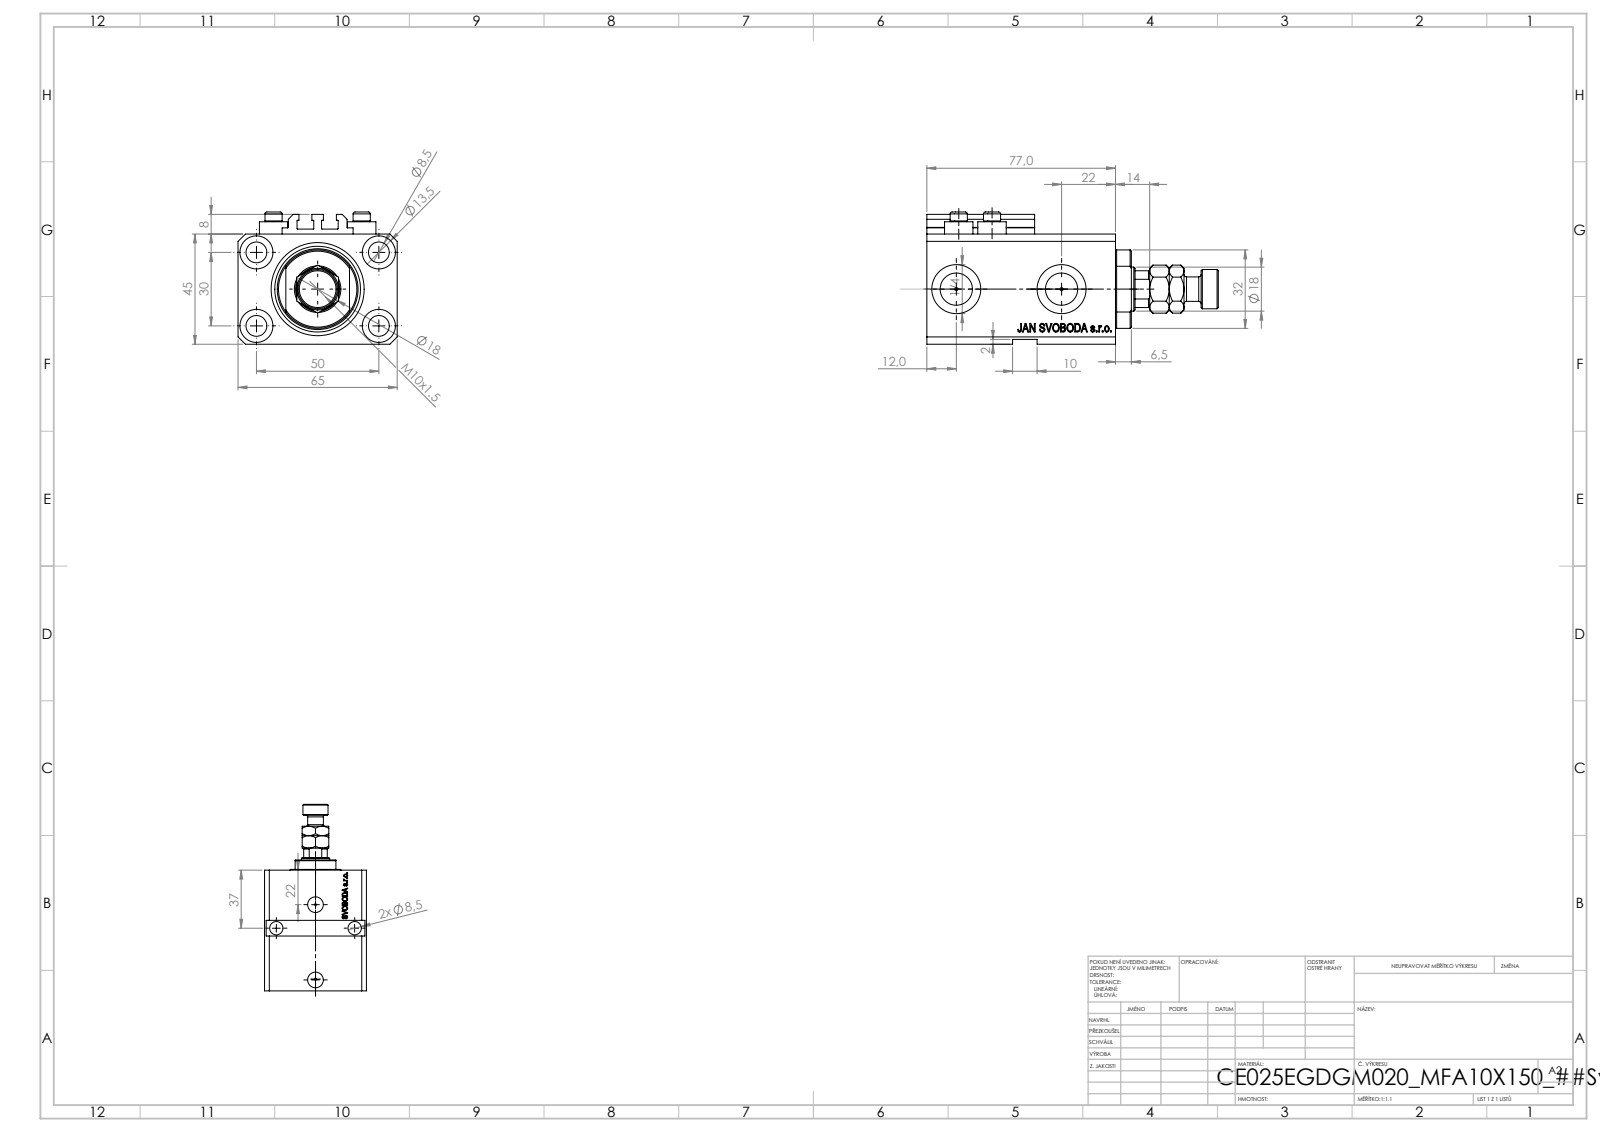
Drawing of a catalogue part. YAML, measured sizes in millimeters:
part_name: "V250CE_E_Body; ALLEN BOLT V250CE; V250CE_VC_E; V250CE_C_VCP (+1 more)"
step_written_by: "SolidWorks 2019 (CONFIG_CONTROL_DESIGN)"
units: millimeters
bodies: {solids: 9, faces: 1135, planar: 531, cylindrical: 142, other: 462}
overall_size: [119, 65, 54]
volume: 201584
surface_area: 62387
round_holes:
  - {diameter: 8.5, count: 7}
  - {diameter: 1.25, count: 4}
  - {diameter: 4, count: 4}
  - {diameter: 13.5, count: 4}
  - {diameter: 10, count: 2}
  - {diameter: 13.16, count: 2}
  - {diameter: 20, count: 2}
  - {diameter: 18, count: 1}
  - {diameter: 25, count: 1}
  - {diameter: 38, count: 1}
round_bosses_or_shafts:
  - {diameter: 11.6, count: 4}
  - {diameter: 7, count: 4}
  - {diameter: 16, count: 1}
  - {diameter: 10, count: 1}
partial_cylinders:
  - {radius: 0.2, count: 10}
  - {radius: 8.5, count: 1}
  - {radius: 16, count: 1}
face_to_face_distances: [45, 65, 14, 63, 77, 2, 6.9, 56.1, 70.1, 20.5]
hole_center_spacings: [29.15, 50, 13.6, 15.12, 18.81, 18.97, 26.22, 26.61]
